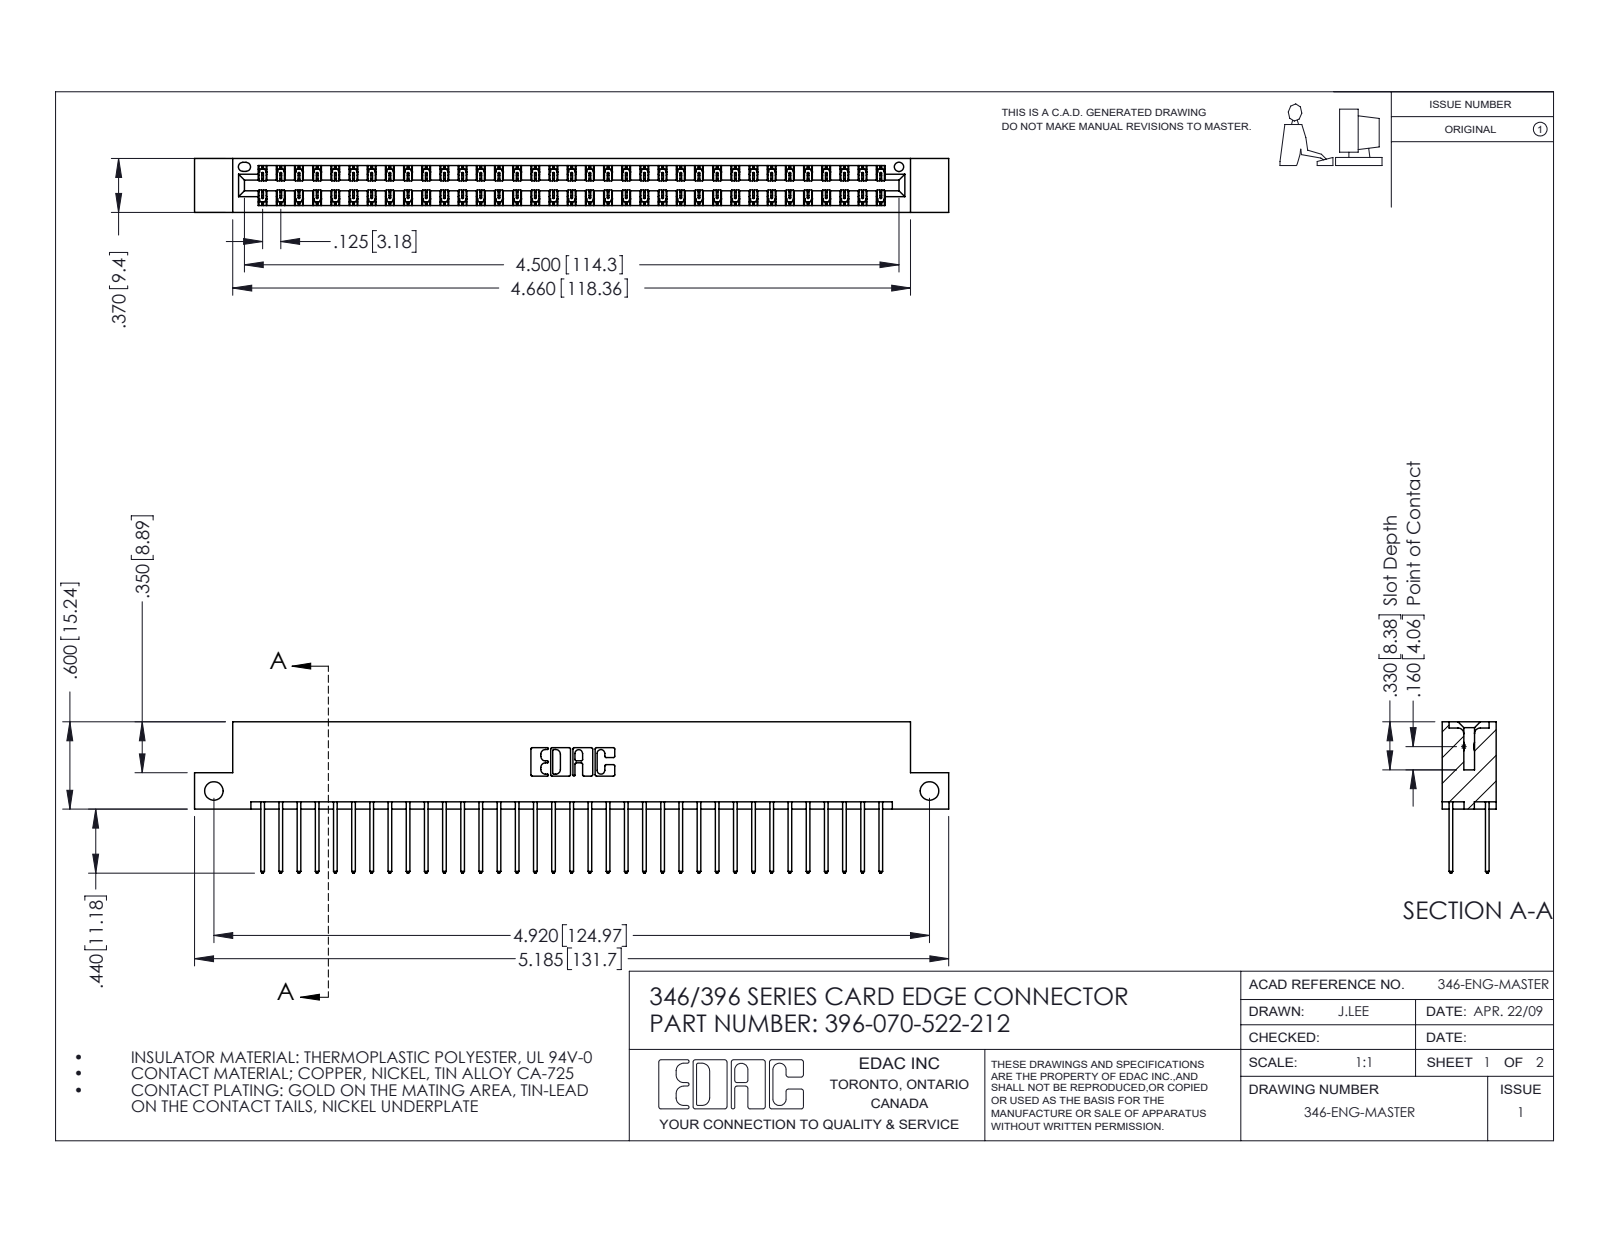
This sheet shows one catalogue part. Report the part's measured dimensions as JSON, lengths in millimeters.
{"part_name": "345-292-001_345-293-122; 346 Part_Flush Mounting Lugs - Side Mount; 396-070-522-212", "step_written_by": "SolidWorks 2016 (CONFIG_CONTROL_DESIGN)", "units": "millimeters", "bodies": {"solids": 71, "faces": 3762, "planar": 2526, "cylindrical": 1236, "other": 0}, "overall_size": [131.7, 26.4, 9.4], "volume_mm3": 12900, "surface_area_mm2": 18290, "round_holes": [[3.3, 2], [1.6, 1]], "partial_cylinders_radius": [[0.2, 105], [0.3, 70], [0.3, 22], [0.2, 6], [0.8, 6], [0.7, 3], [0.4, 2], [0.6, 2]], "face_to_face_distances": [1.2, 8.2, 6.4, 9.4, 1.8, 7.6, 0.6, 7, 3.8, 5.6], "hole_center_spacings": [125]}
